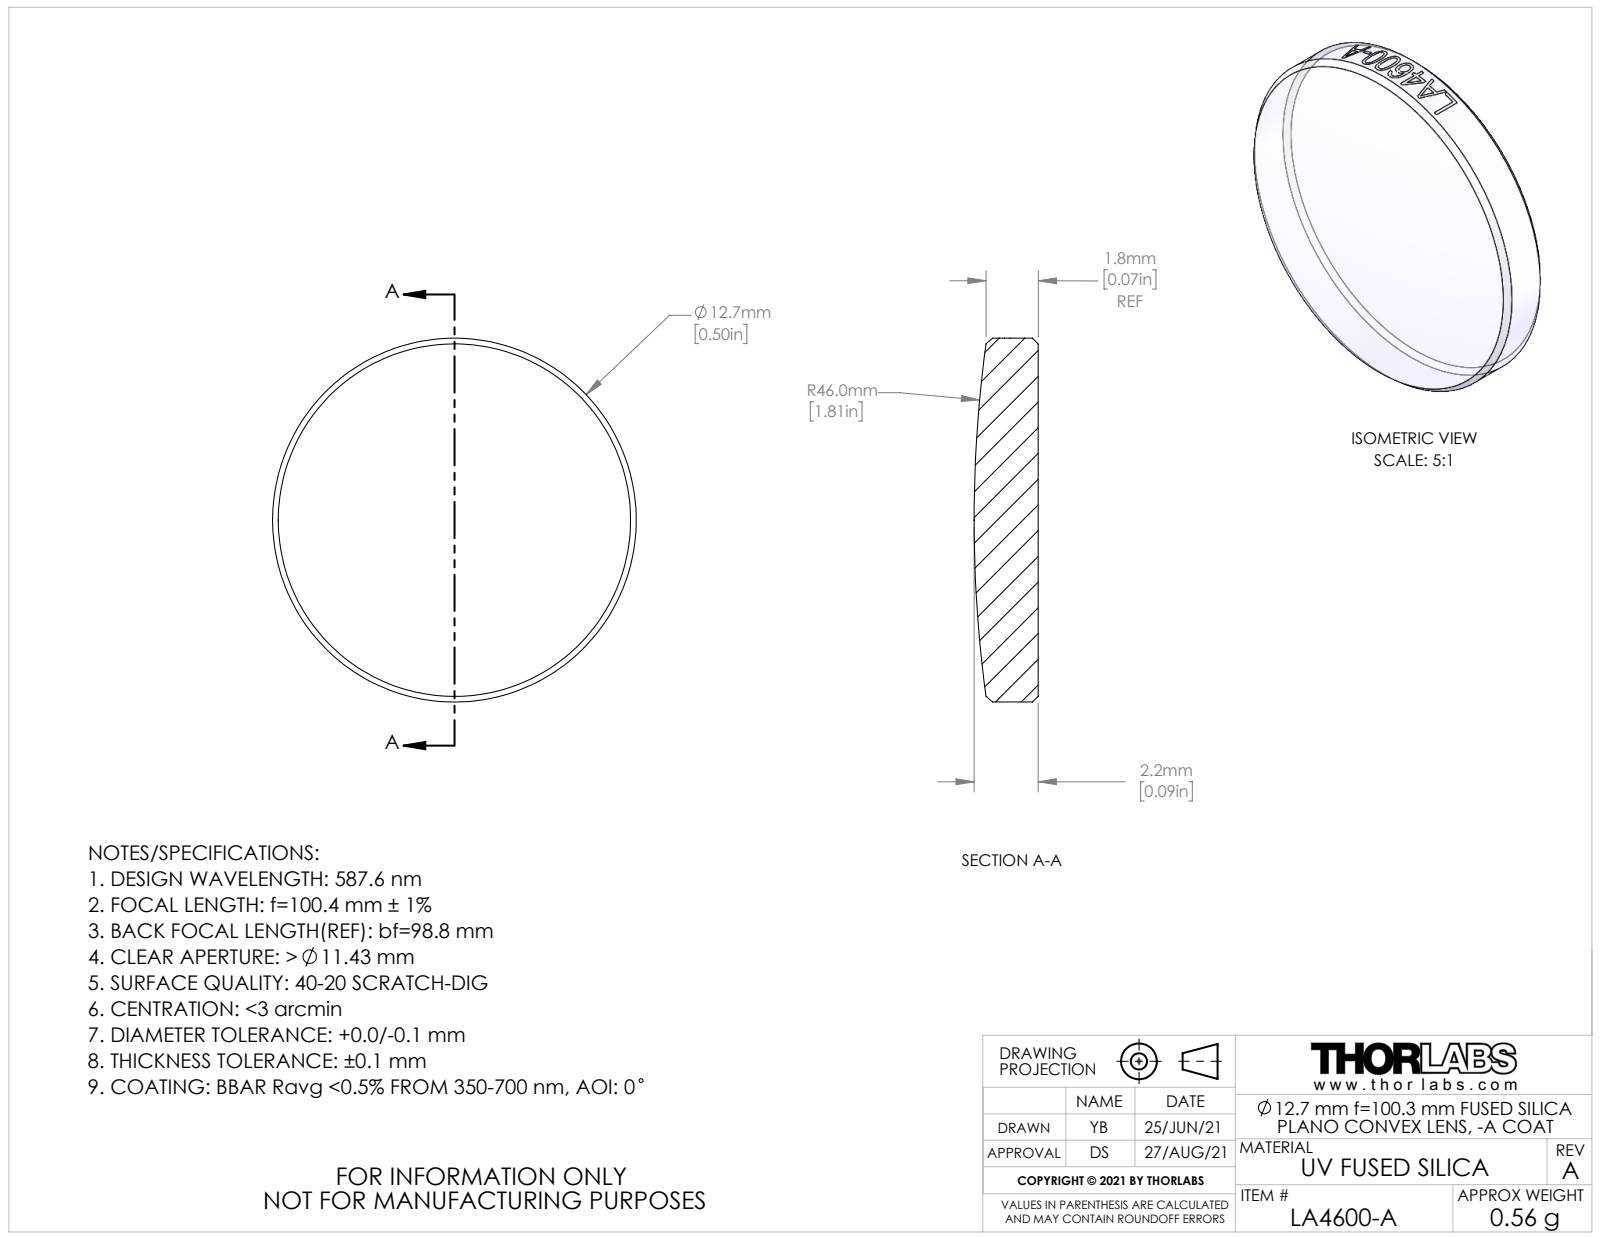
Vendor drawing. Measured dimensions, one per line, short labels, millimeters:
name: CTN017531-E0W; CTN017559
written by: SolidWorks 2018 (AUTOMOTIVE_DESIGN)
unit: mm
bodies: 1 solid, 23 faces (1 planar, 16 cylindrical, 6 other)
size: 12.7 × 12.7 × 2.24
volume: 254 mm³; area: 317 mm²
bosses: 1× ⌀12.7
